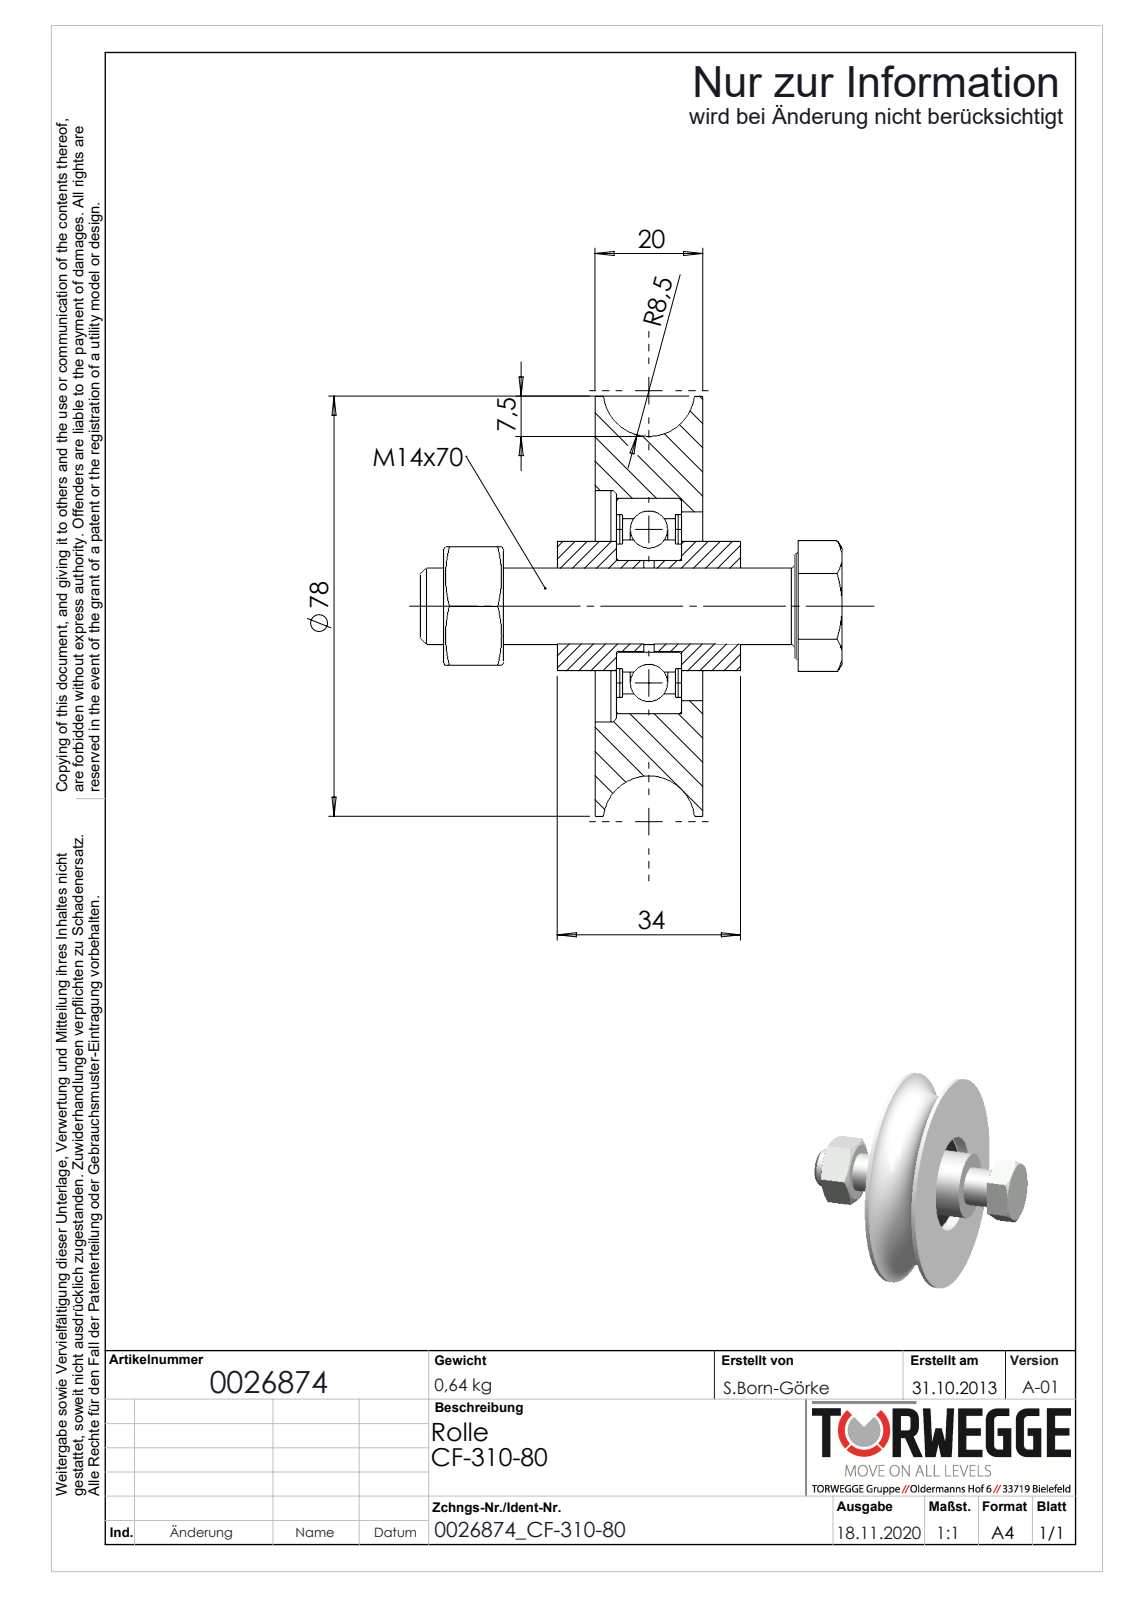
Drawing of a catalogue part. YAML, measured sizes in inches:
part_name: "0026874"
step_written_by: "SolidWorks 2018 (AUTOMOTIVE_DESIGN)"
units: inches
bodies: {solids: 10, faces: 140, planar: 40, cylindrical: 54, other: 46}
overall_size: [3.079, 3.071, 3.071]
volume: 5.141
surface_area: 57.11
round_holes:
  - {diameter: 0.466, count: 1}
  - {diameter: 0.551, count: 1}
  - {diameter: 0.669, count: 1}
  - {diameter: 0.909, count: 1}
  - {diameter: 1.28, count: 1}
  - {diameter: 1.335, count: 1}
  - {diameter: 1.378, count: 1}
  - {diameter: 1.575, count: 1}
  - {diameter: 1.693, count: 1}
round_bosses_or_shafts:
  - {diameter: 3.071, count: 1}
  - {diameter: 0.965, count: 1}
  - {diameter: 0.945, count: 1}
  - {diameter: 0.665, count: 1}
face_to_face_distances: [0.787, 0.63, 0.157, 0.022, 0.472, 0.18, 0.608, 0.45, 0.433, 0.276]
